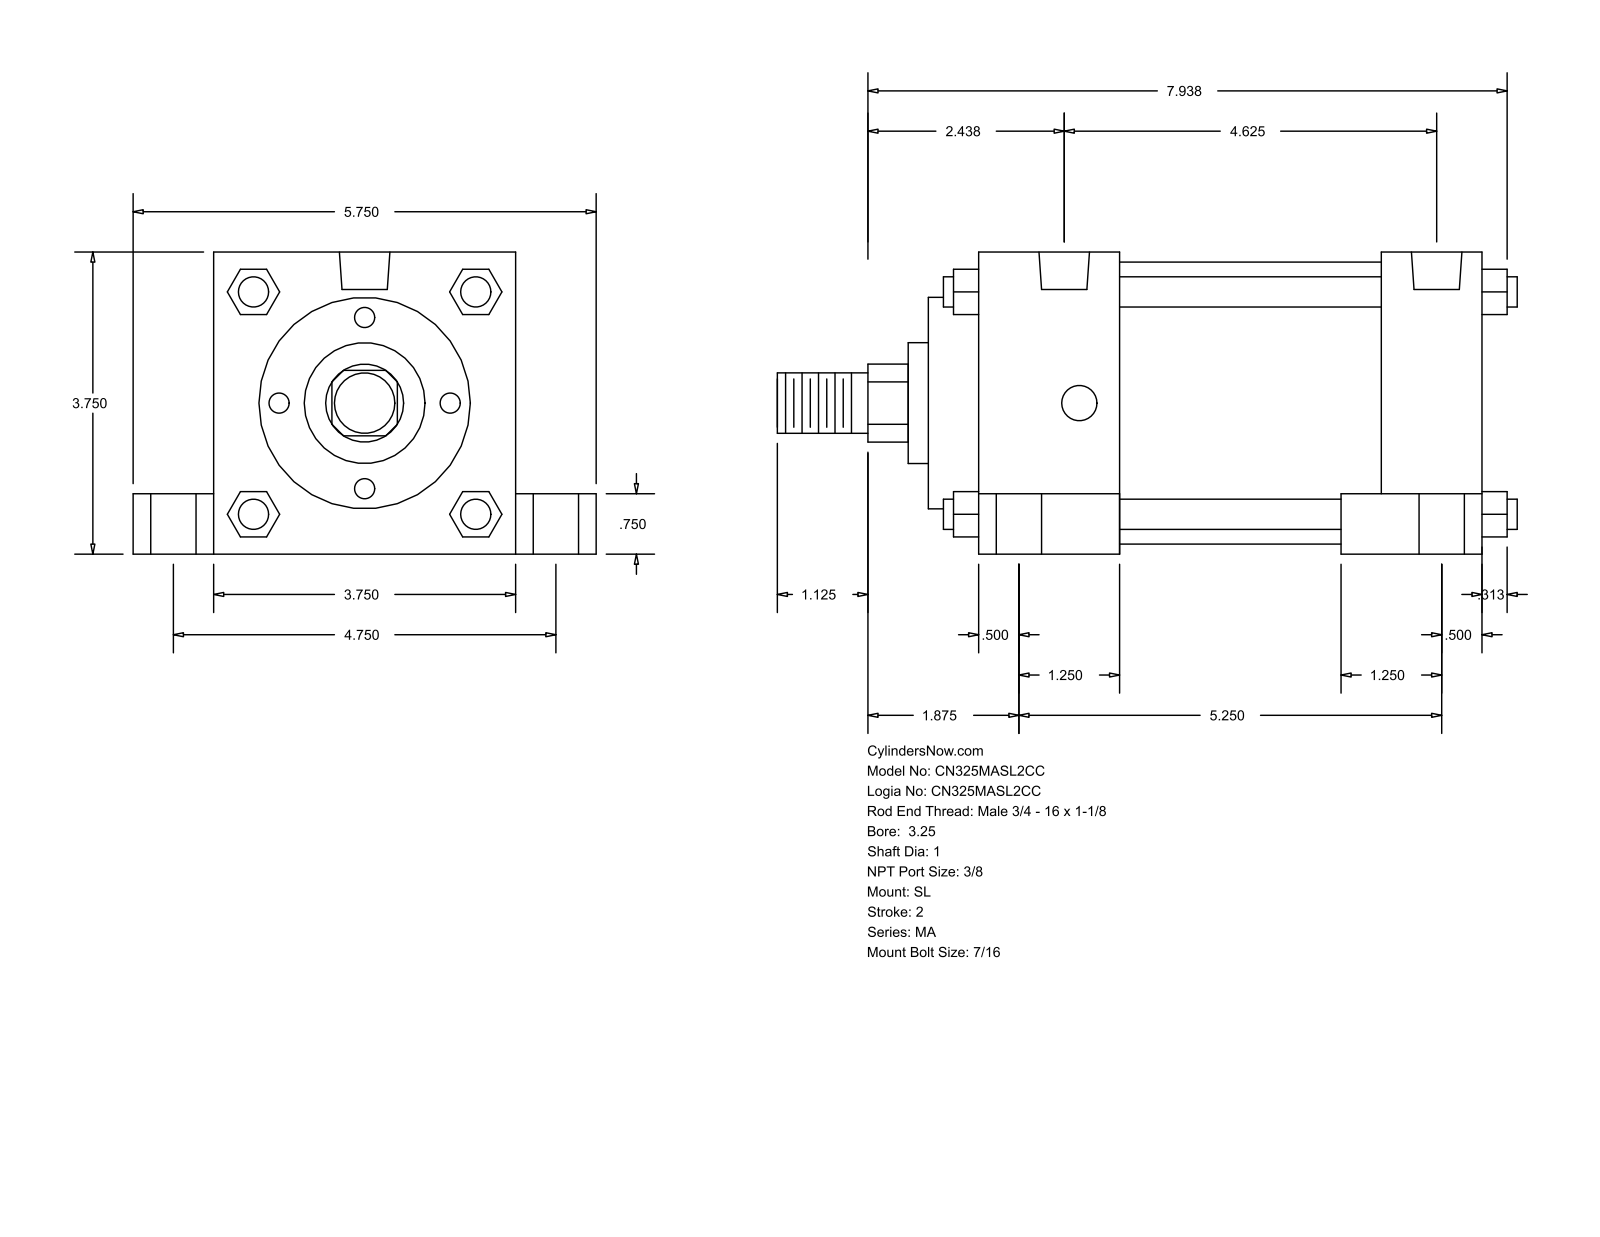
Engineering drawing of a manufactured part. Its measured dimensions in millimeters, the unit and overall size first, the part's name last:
Units: millimetres
Overall size (bounding box): 233.36 × 146.05 × 95.25
Round holes (diameter × count): ⌀11.11 ×4, ⌀14.29 ×4, ⌀20.64 ×4, ⌀15.93 ×2
Round bosses / shafts (diameter × count): ⌀9.53 ×4, ⌀88.9 ×1, ⌀66.67 ×1, ⌀38.1 ×1, ⌀25.4 ×1, ⌀19.05 ×1
Partial cylindrical surfaces — rounded edges, fillets, slot ends (radius × count): R12.29 ×1
Main face-to-face distances: 95.24, 158.76, 82.55, 15.87, 25.41, 120.65, 19.05, 127.01, 31.75, 44.46
Hole centre spacings: 60.35, 60.66, 62, 63.27, 107.95, 120.66, 129.24, 133.35
Bodies: 0 solids, 150 faces (113 planar, 37 cylindrical, 0 other)
Part name (STEP PRODUCT): MA_SL__0325_1
STEP written by: GSSL Pune (CONFIG_CONTROL_DESIGN)
